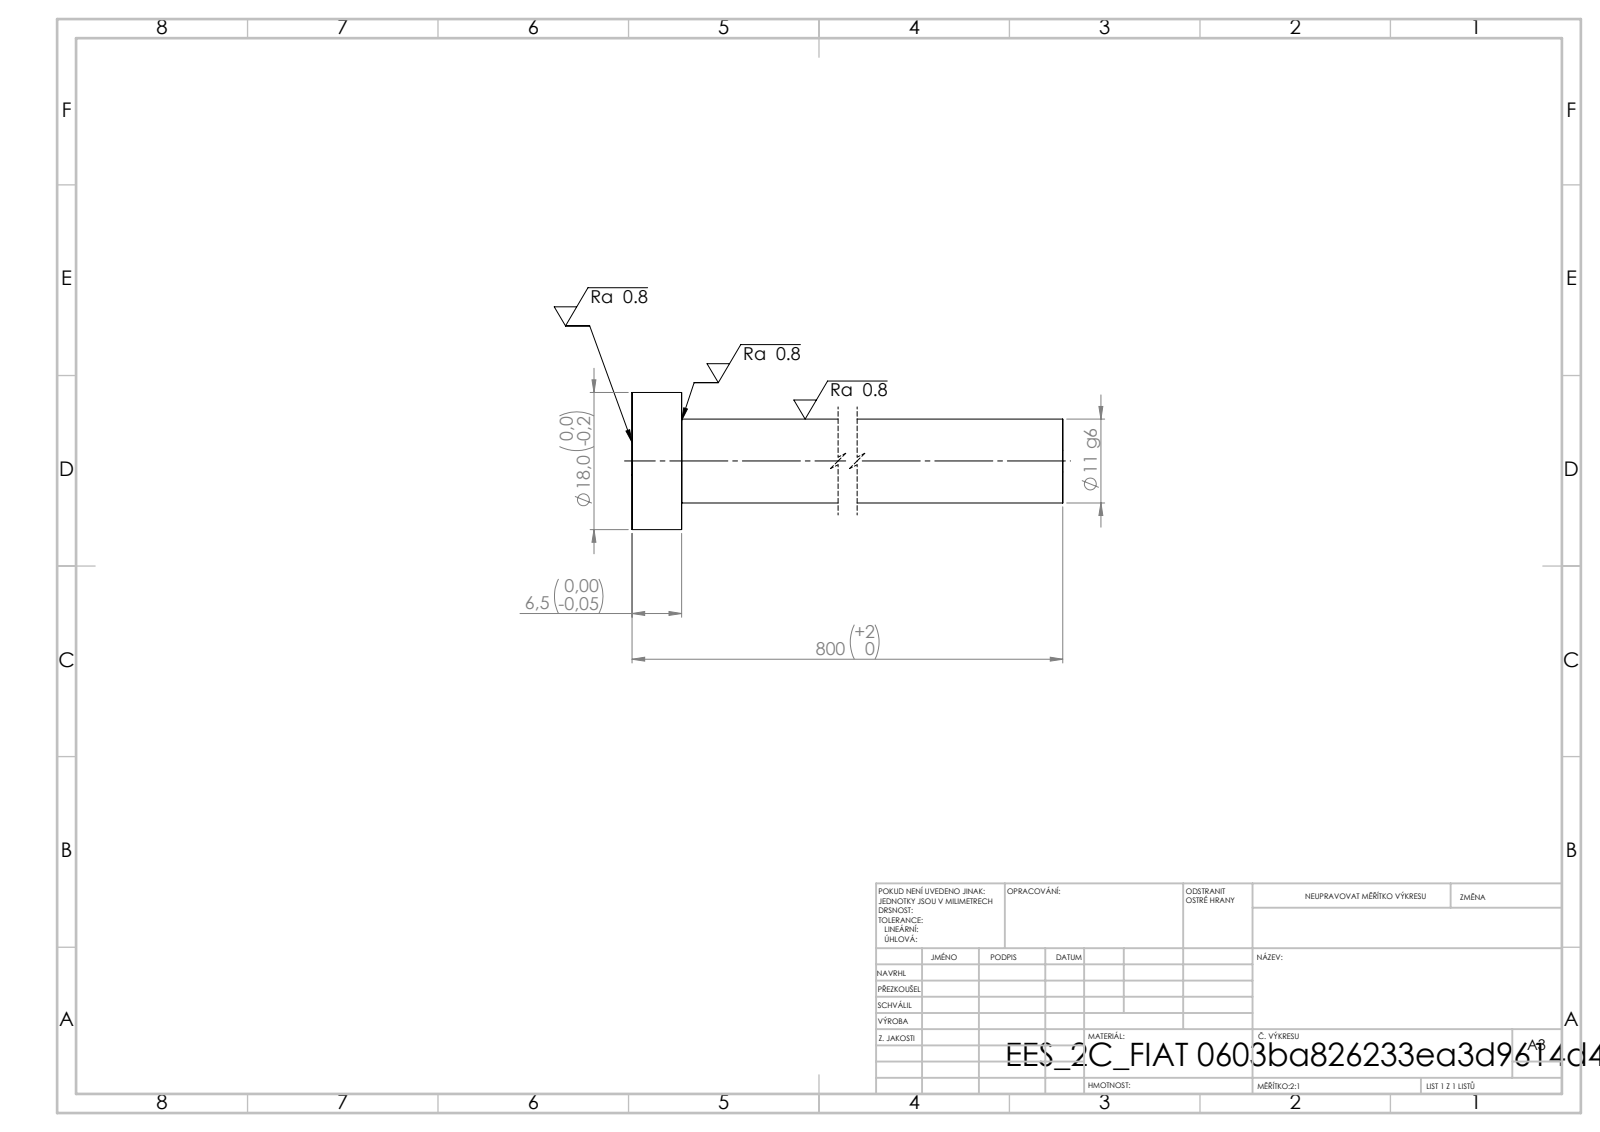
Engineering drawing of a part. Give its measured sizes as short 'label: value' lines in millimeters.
written by: SolidWorks 2019 (CONFIG_CONTROL_DESIGN)
unit: mm
bodies: 1 solid, 7 faces (3 planar, 4 cylindrical, 0 other)
size: 800 × 18 × 18
volume: 77 063 mm³; area: 28 298 mm²
bosses: 1× ⌀18, 1× ⌀11
face distances: 6.5, 800, 793.5
